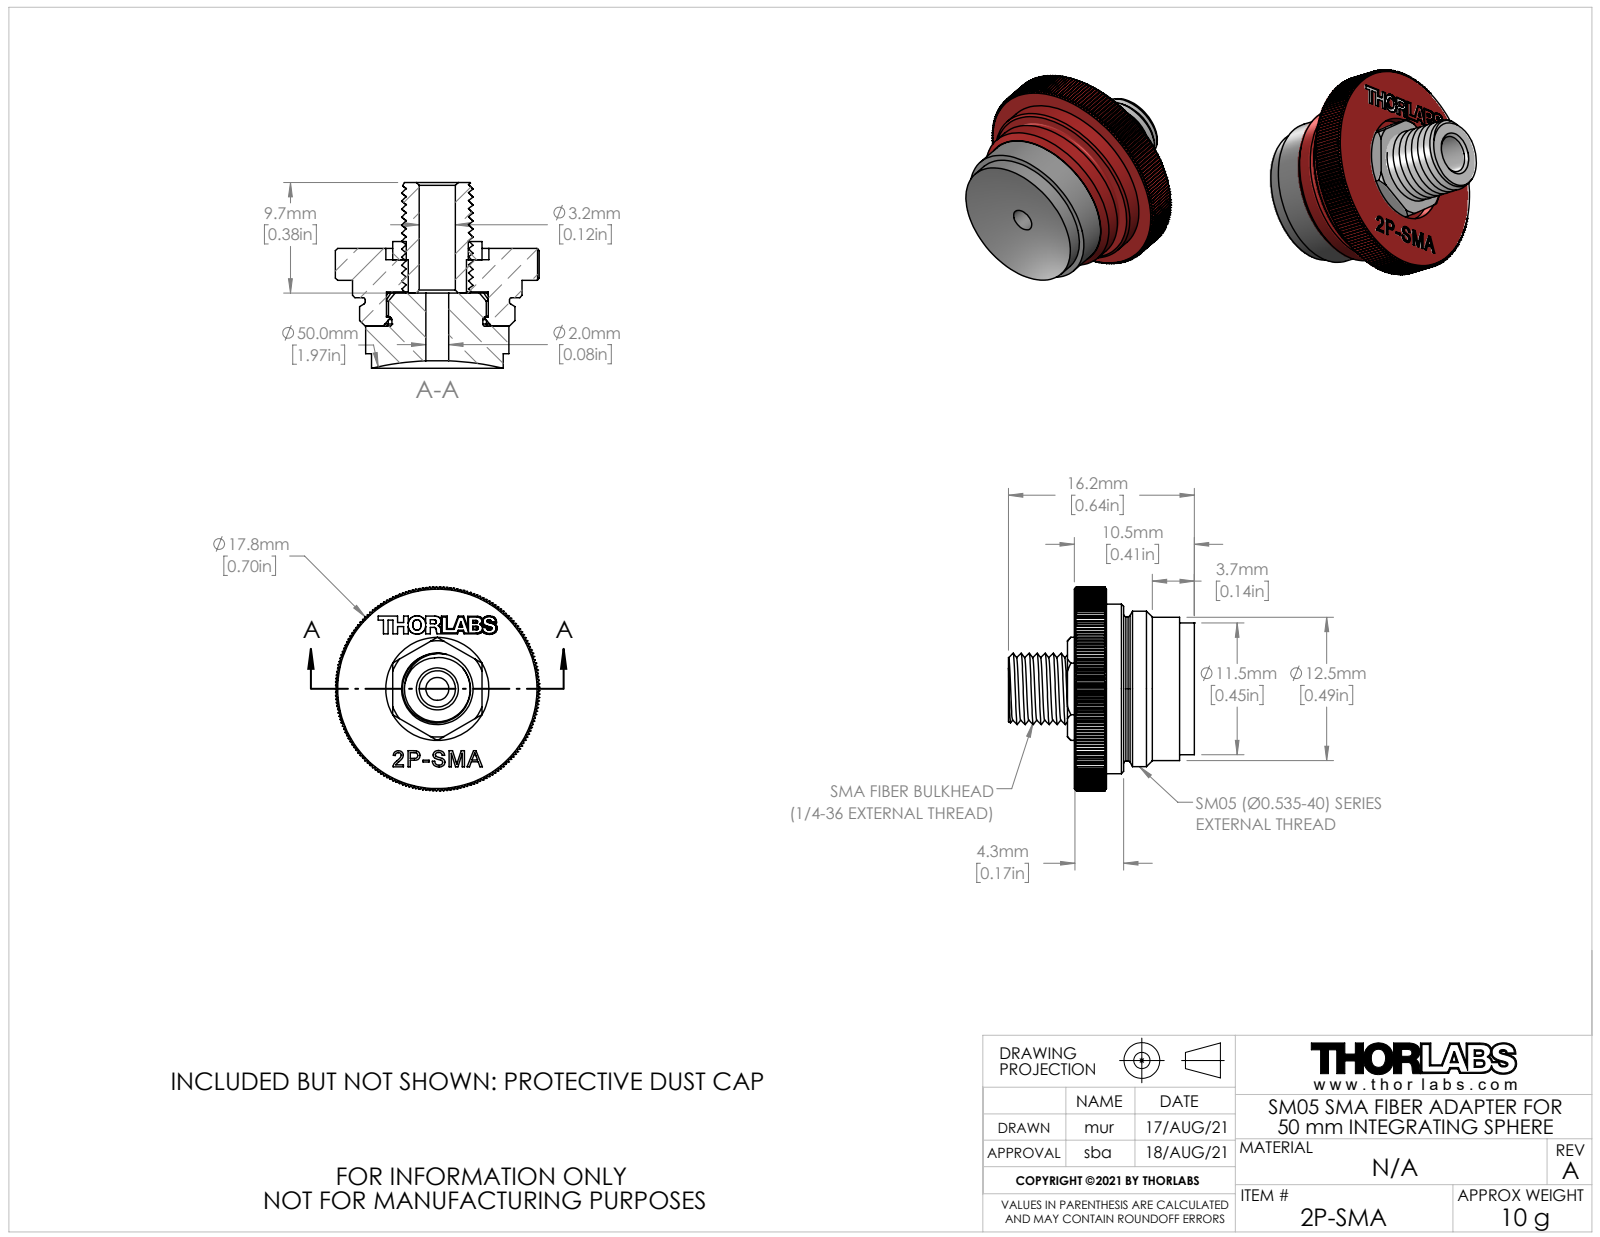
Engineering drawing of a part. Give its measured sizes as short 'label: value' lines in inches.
name: 21.08.19_2P-SMA_SMA-Adapter w. Sphere Radius_WEB
written by: SolidWorks 2019 (AUTOMOTIVE_DESIGN)
unit: in
bodies: 4 solids, 1277 faces (916 planar, 236 cylindrical, 125 other)
size: 0.701 × 0.701 × 0.639
volume: 0.105 in³; area: 3.216 in²
holes: 1× ⌀0.079, 1× ⌀0.124, 1× ⌀0.2, 1× ⌀0.213, 1× ⌀0.354
bosses: 1× ⌀0.583, 1× ⌀0.534, 1× ⌀0.496, 1× ⌀0.492, 1× ⌀0.453
rounds: 4× R0.067, 4× R0.07, 4× R0.079, 2× R0.041, 2× R0.05, 2× R0.053, 1× R0.209, 1× R0.212
face distances: 0.11, 0.039, 0.114, 0.15, 0.154, 0.071, 0.043, 0.118, 0.157, 0.268
